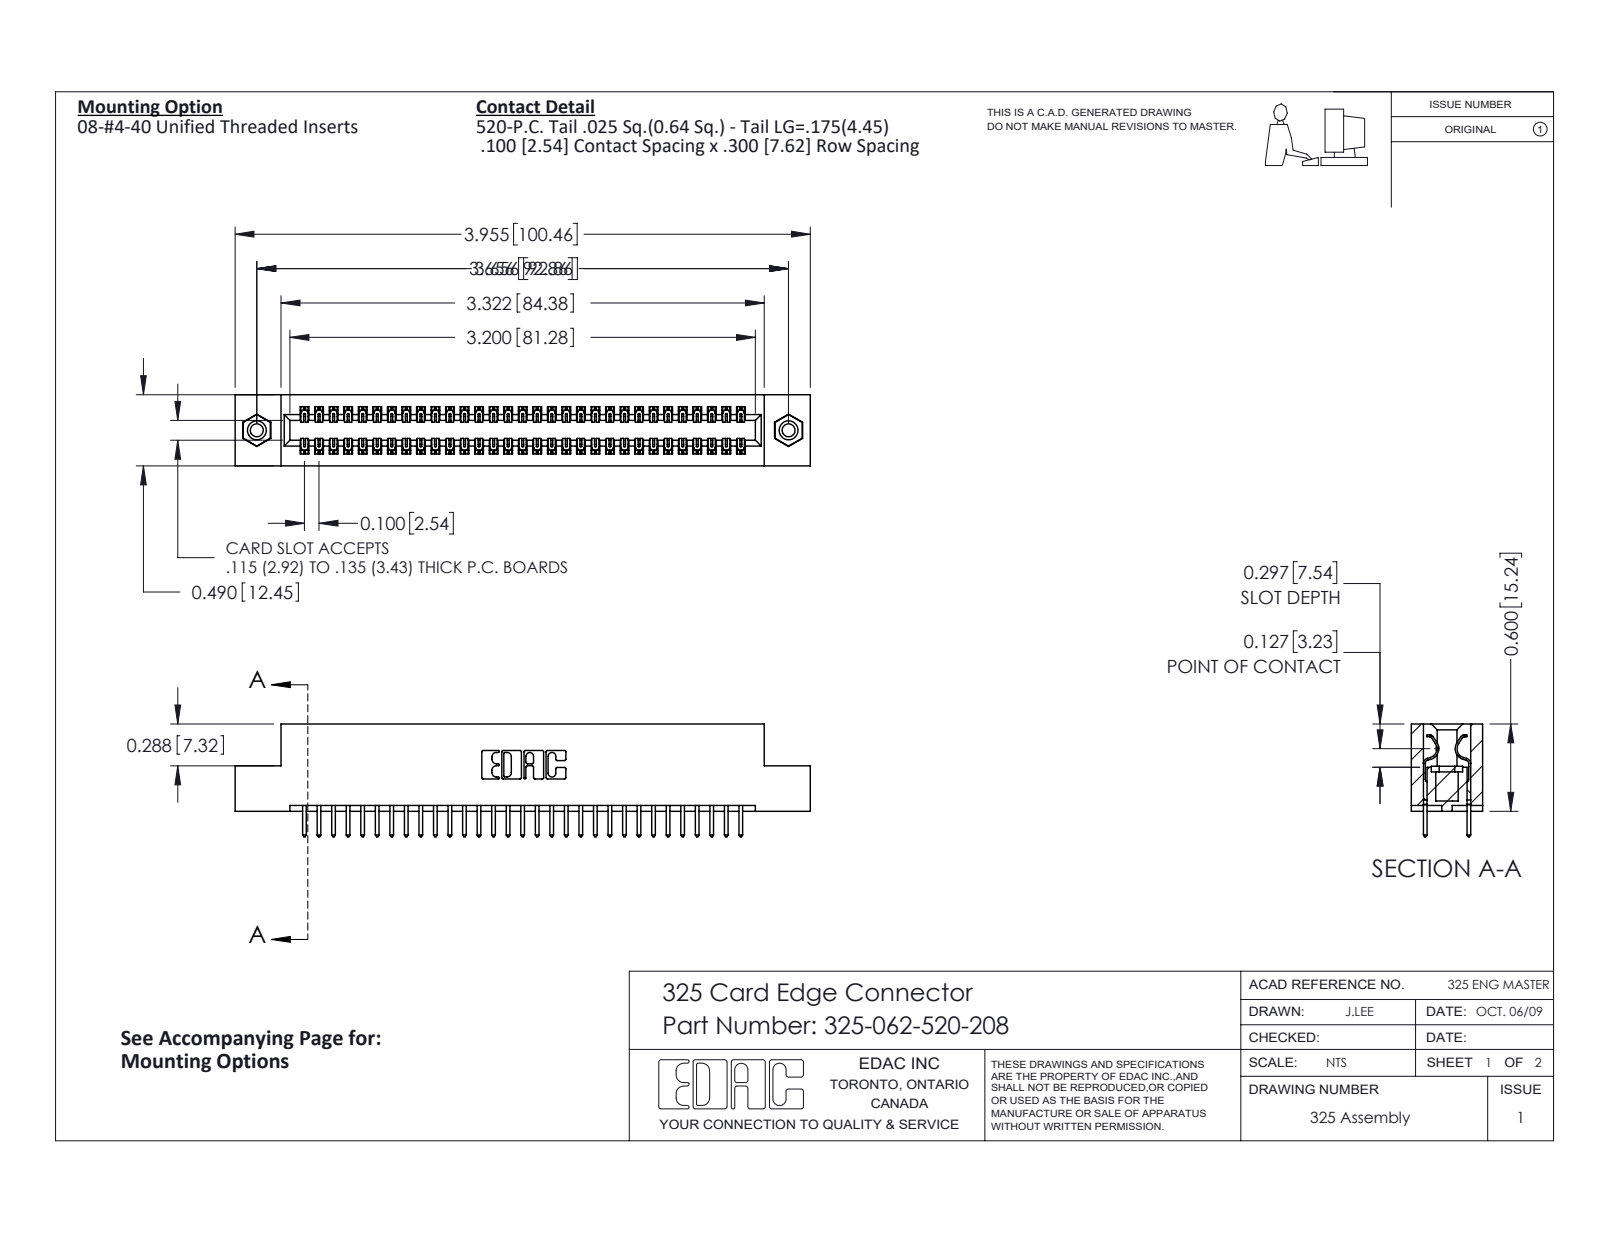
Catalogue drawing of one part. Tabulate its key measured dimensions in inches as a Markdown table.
| quantity | value |
| --- | --- |
| part name | 325 Part_TI; 345-250-001_345-250-003-102; 325-292-001_325-293-120; 325-062-520-208 |
| STEP written by | SolidWorks 2016 (CONFIG_CONTROL_DESIGN) |
| units | inches |
| bodies | 65 solids, 3398 faces (2334 planar, 1048 cylindrical, 16 other) |
| overall size | 3.955 × 0.775 × 0.49 |
| volume | 0.784 in³ |
| surface area | 23.54 in² |
| round holes (diameter × count) | 0.089 × 2, 0.125 × 2, 0.16 × 2 |
| round bosses / shafts (diameter × count) | 0.155 × 2 |
| partial cylindrical surfaces (radius × count) | 0.006 × 93, 0.01 × 62, 0.01 × 22, 0.007 × 6, 0.031 × 6, 0.026 × 3, 0.014 × 2, 0.022 × 2 |
| main face-to-face distances | 0.083, 0.407, 0.3, 0.49, 0.107, 0.383, 0.025, 0.325, 0.04, 0.275 |
| hole center spacings | 3.656 |
